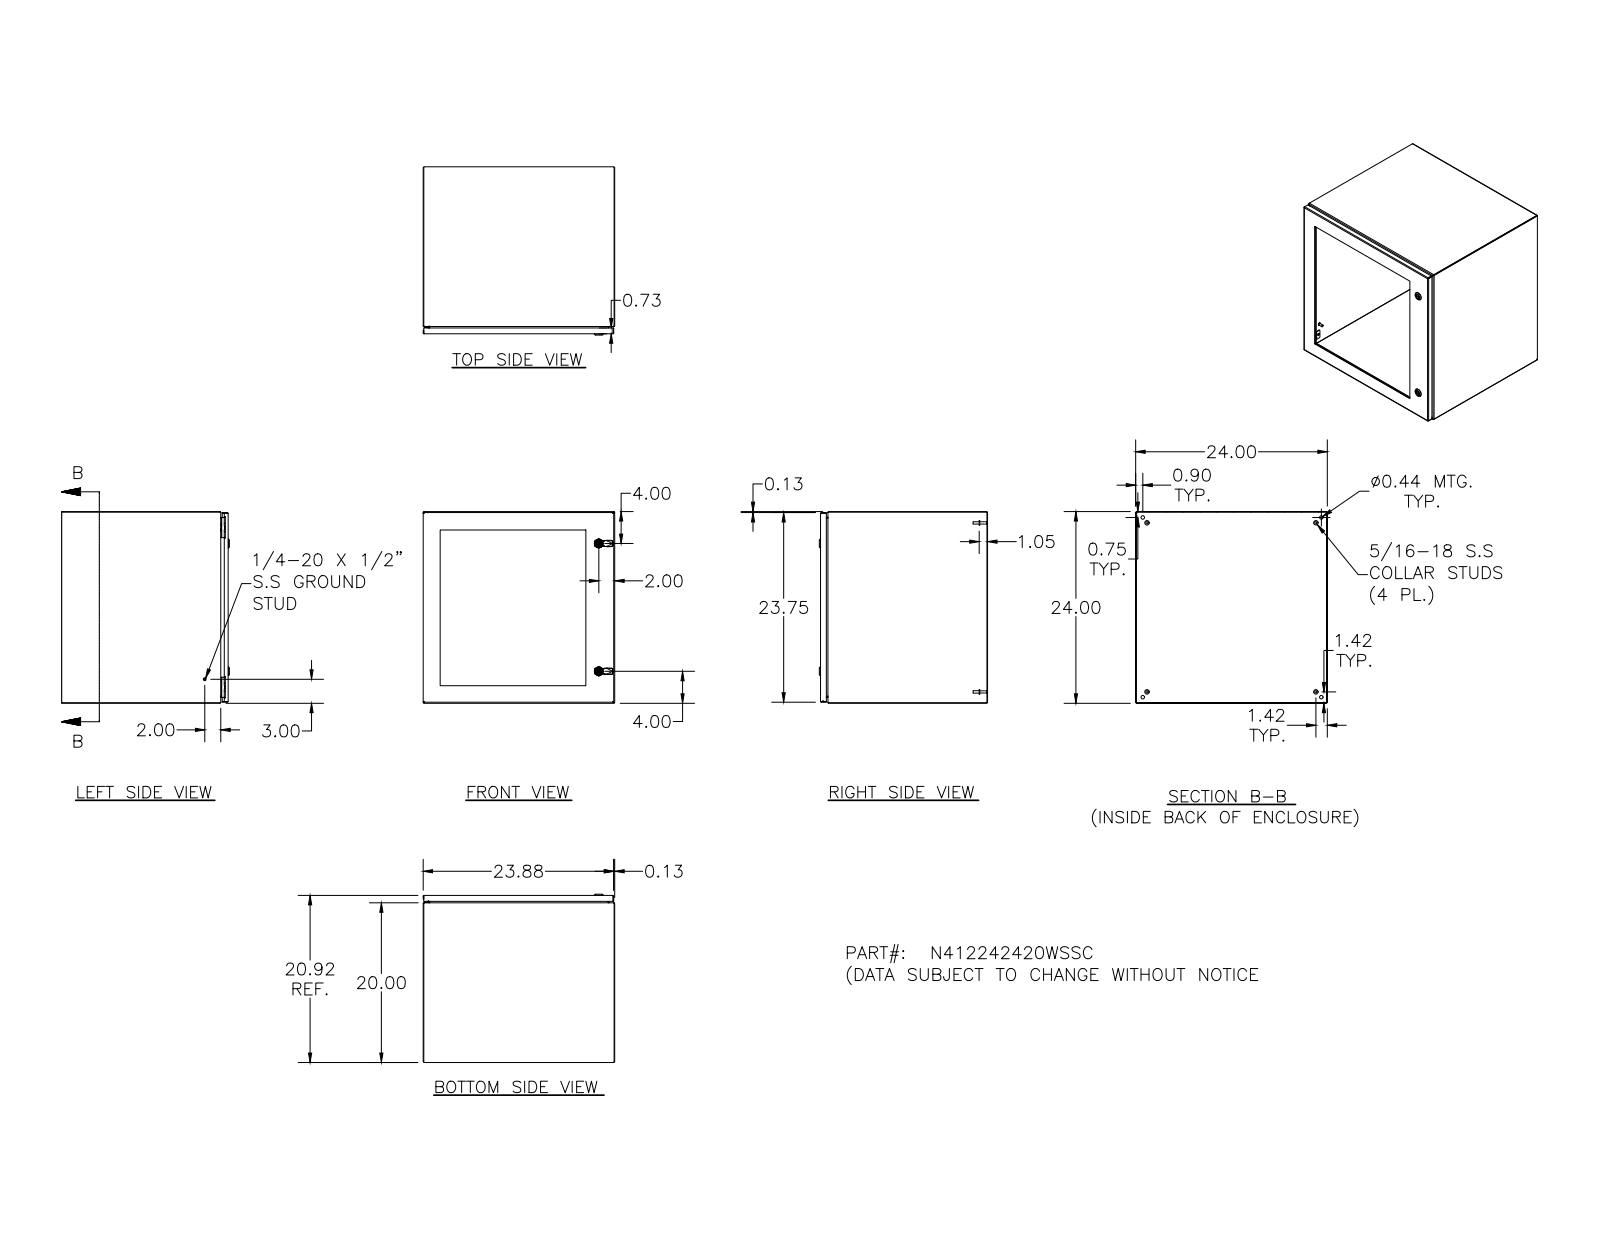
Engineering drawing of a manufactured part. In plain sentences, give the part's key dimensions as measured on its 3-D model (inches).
The part is named "N412242420WSSC; N4122424WSSCLID; 36823; 36824 (+8 more)". Its 3-D file was written by "Autodesk Inventor 2011 (AUTOMOTIVE_DESIGN)". It is 88 solids with 2378 faces: 997 planar, 668 cylindrical and 713 other. Overall it measures 24 by 24 by 21.075 inches. Its volume is 320.5 cubic inches and its surface area 6 857 square inches. Round holes: 22 of diameter 0.156, 20 of diameter 0.281, 4 of diameter 0.093, 4 of diameter 0.152, 4 of diameter 0.167, 4 of diameter 0.172, 4 of diameter 0.187, 4 of diameter 0.437, 2 of diameter 0.197, 2 of diameter 0.315, 2 of diameter 0.394, 2 of diameter 0.402. Round bosses or shafts: 20 of diameter 0.19, 19 of diameter 0.253, 10 of diameter 0.25, 4 of diameter 0.563, 4 of diameter 0.36, 4 of diameter 0.32, 4 of diameter 0.3, 4 of diameter 0.275. Partial cylindrical surfaces (rounded edges, fillets, slot ends): 32 of radius 0.031, 26 of radius 0.05, 22 of radius 0.105, 18 of radius 0.016, 16 of radius 0.125, 15 of radius 0.02, 8 of radius 0.032, 8 of radius 0.157. The main face-to-face distances are 0.074, 23.926, 23.852, 24, 20.843, 20.769, 0.25, 20.593, 20.519, 20.917. The hole center spacings are 4, 8, 12, 19.906, 21.132, 21.077, 22.239, 16.
